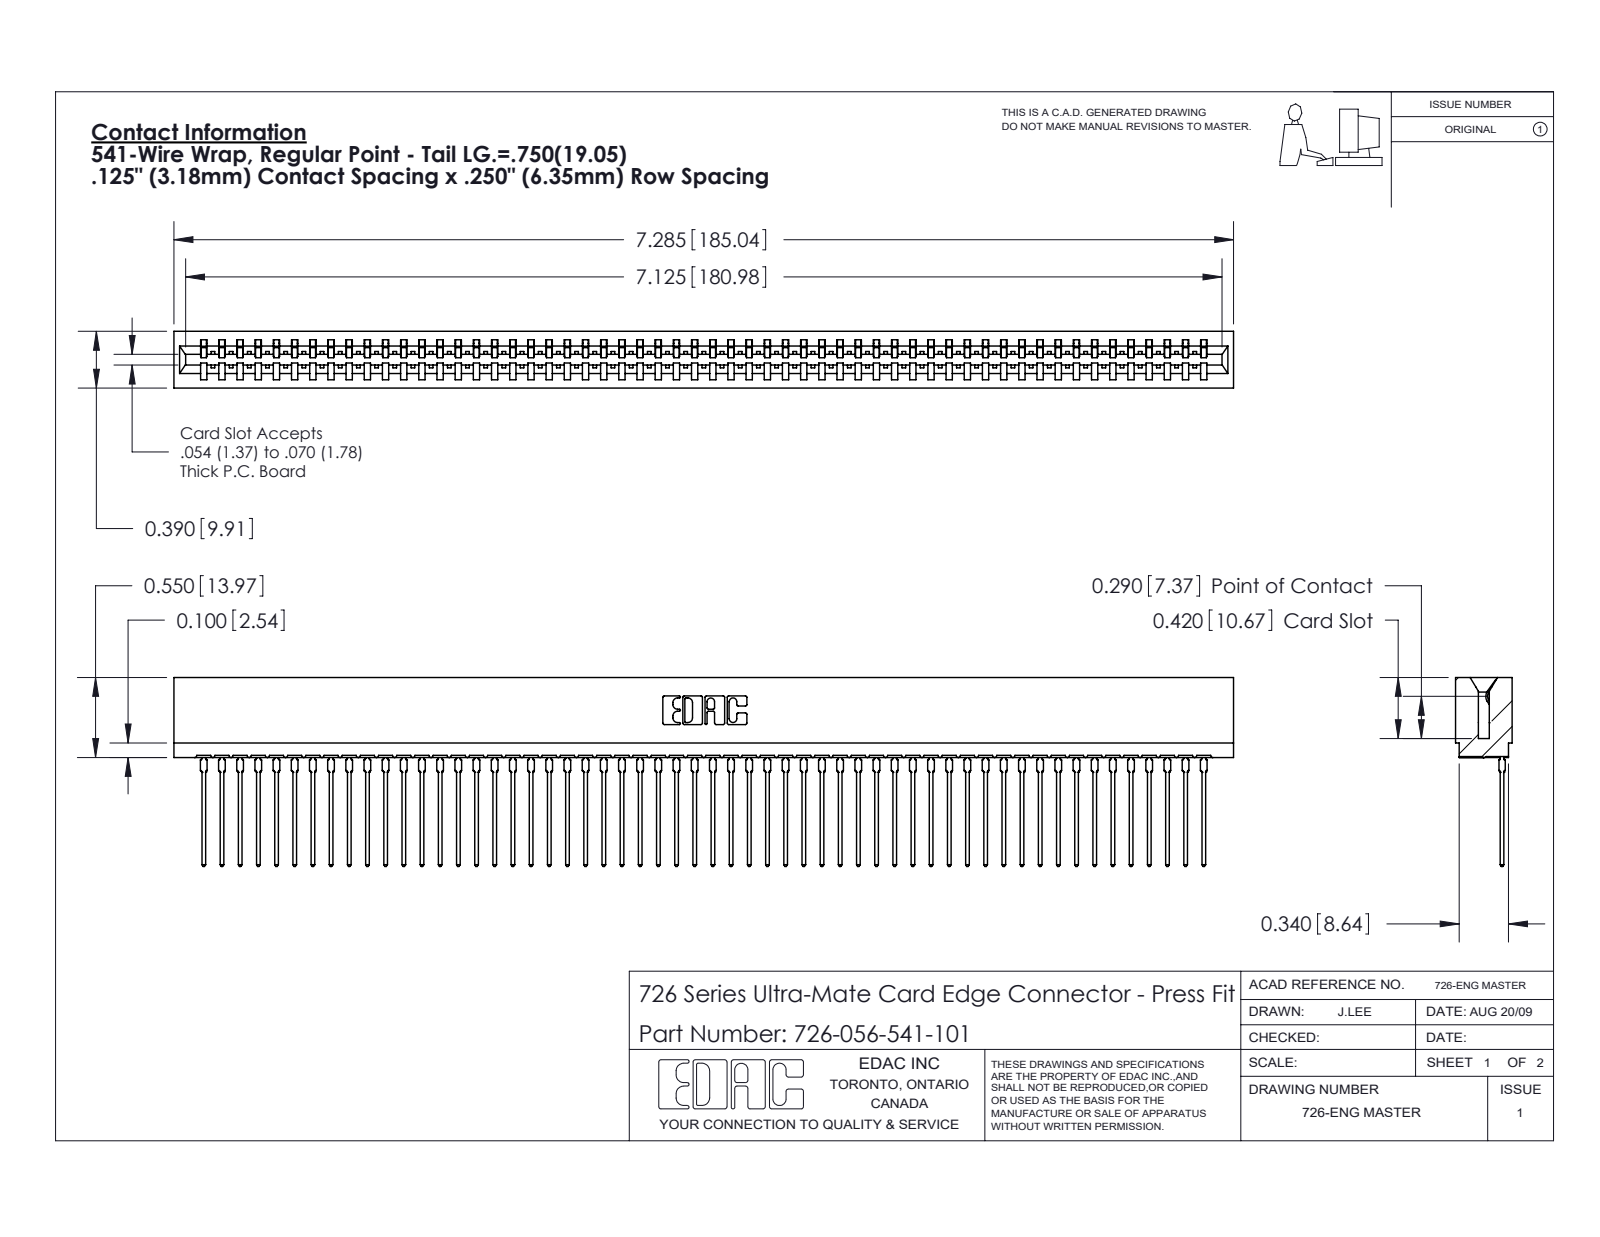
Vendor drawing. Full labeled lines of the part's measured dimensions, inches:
Part name (STEP PRODUCT): 746-292-001_541; 726 Part_.515 Slot Depth - 01; 726-056-541-101
STEP written by: SolidWorks 2020 (CONFIG_CONTROL_DESIGN)
Units: inches
Bodies: 57 solids, 6145 faces (3583 planar, 1106 cylindrical, 1456 other)
Overall size (bounding box): 7.285 × 1.299 × 0.39
Volume: 1.02 in³ · Surface area: 41.92 in²
Partial cylindrical surfaces — rounded edges, fillets, slot ends (radius × count): R0.021 ×112, R0.015 ×57, R0.01 ×22, R0.007 ×6, R0.031 ×6, R0.005 ×4, R0.011 ×4, R0.026 ×3
Main face-to-face distances: 0.057, 0.333, 0.39, 0.025, 0.307, 0.25, 0.083, 0.275, 0.365, 0.032
